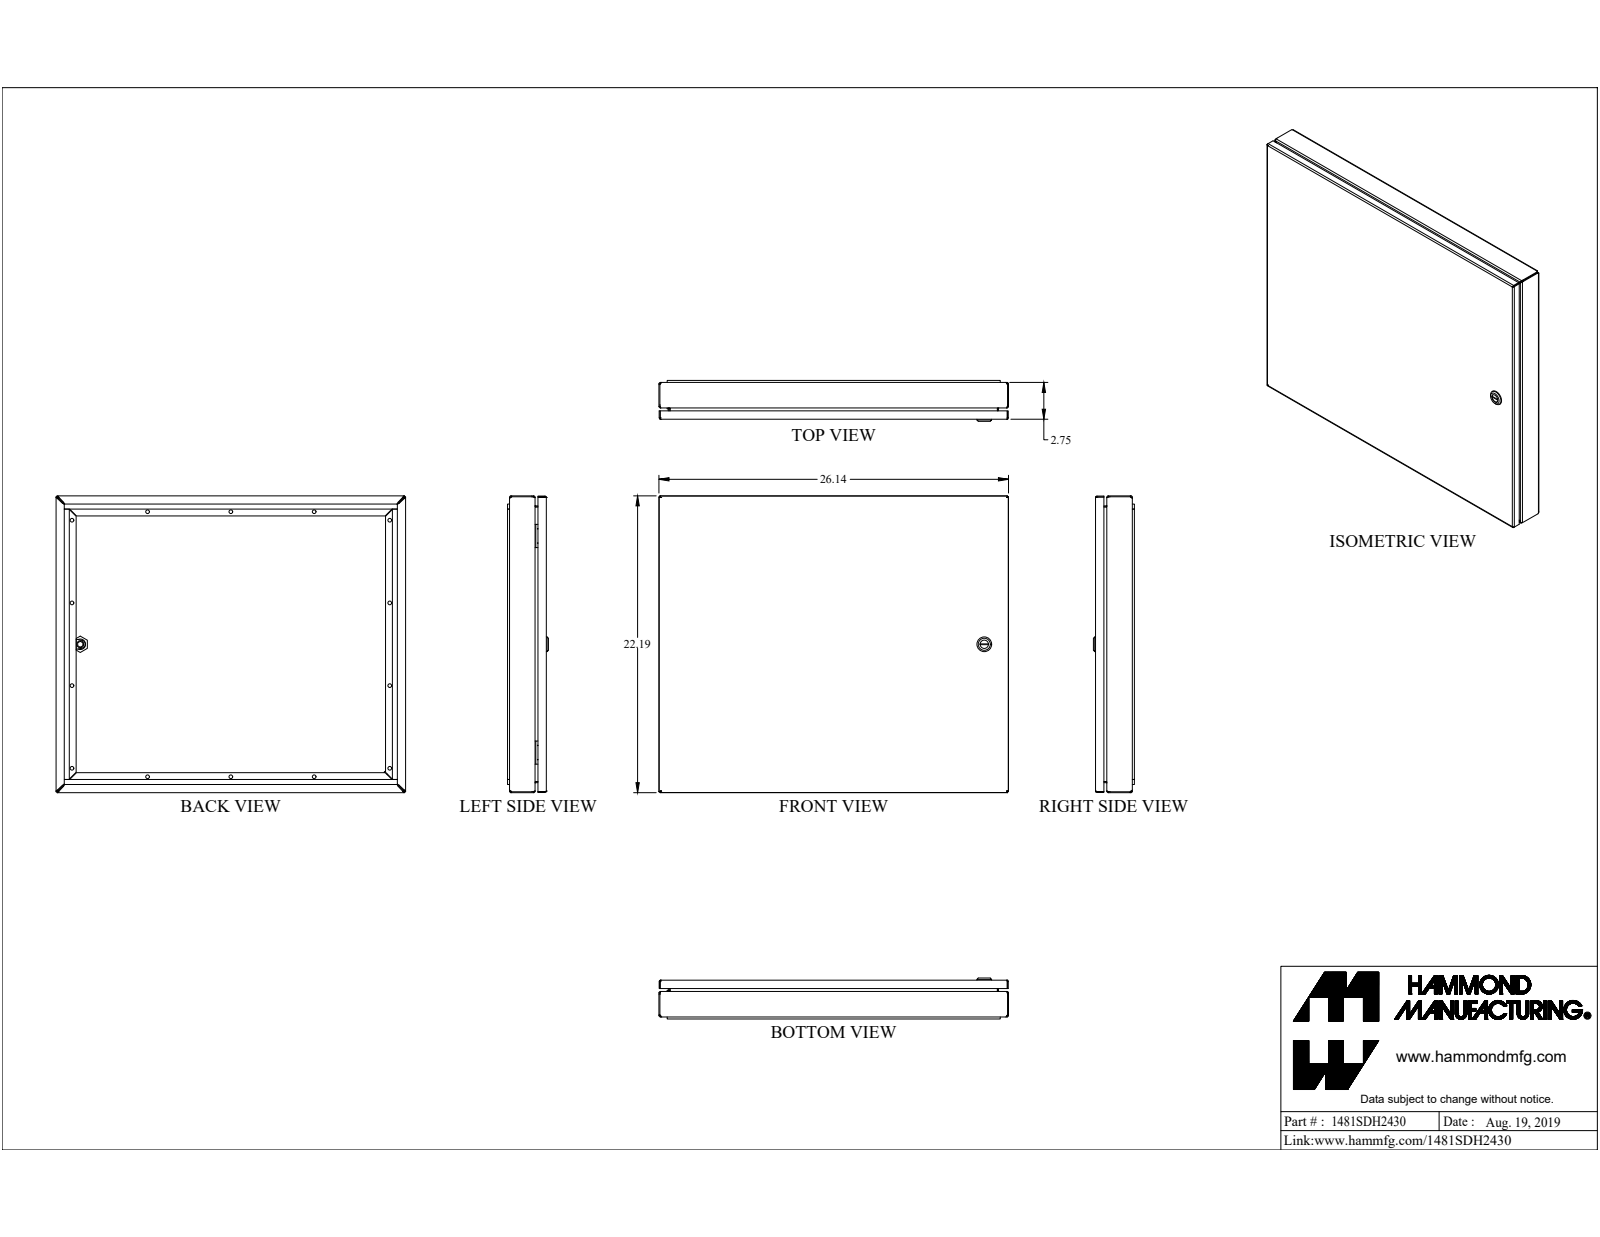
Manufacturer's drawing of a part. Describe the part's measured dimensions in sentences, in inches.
The part is named "1481SDH2430". Its 3-D file was written by "SolidWorks 2019 (CONFIG_CONTROL_DESIGN)". It is 23 solids with 620 faces: 348 planar, 174 cylindrical and 98 other. Overall it measures 26.14 by 22.19 by 3.061 inches. Its volume is 95.25 cubic inches and its surface area 2 502 square inches. Round holes: 14 of diameter 0.281, 1 of diameter 0.172, 1 of diameter 0.232, 1 of diameter 0.24, 1 of diameter 0.242, 1 of diameter 0.625, 1 of diameter 0.785. Round bosses or shafts: 1 of diameter 1.1, 1 of diameter 0.525, 1 of diameter 0.455, 1 of diameter 0.398, 1 of diameter 0.356, 1 of diameter 0.313, 1 of diameter 0.292, 1 of diameter 0.25. Partial cylindrical surfaces (rounded edges, fillets, slot ends): 28 of radius 0.036, 28 of radius 0.108, 12 of radius 0.382, 8 of radius 19.003, 4 of radius 0.006, 4 of radius 0.062, 4 of radius 0.25, 4 of radius 0.499. The main face-to-face distances are 0.072, 2.579, 0.843, 1.736, 2.651, 22.118, 2.507, 26.068, 2.679, 1.836. The hole center spacings are 24.555, 5.687, 6.182, 6.23, 11.899, 13.698, 18.123, 19.352.
